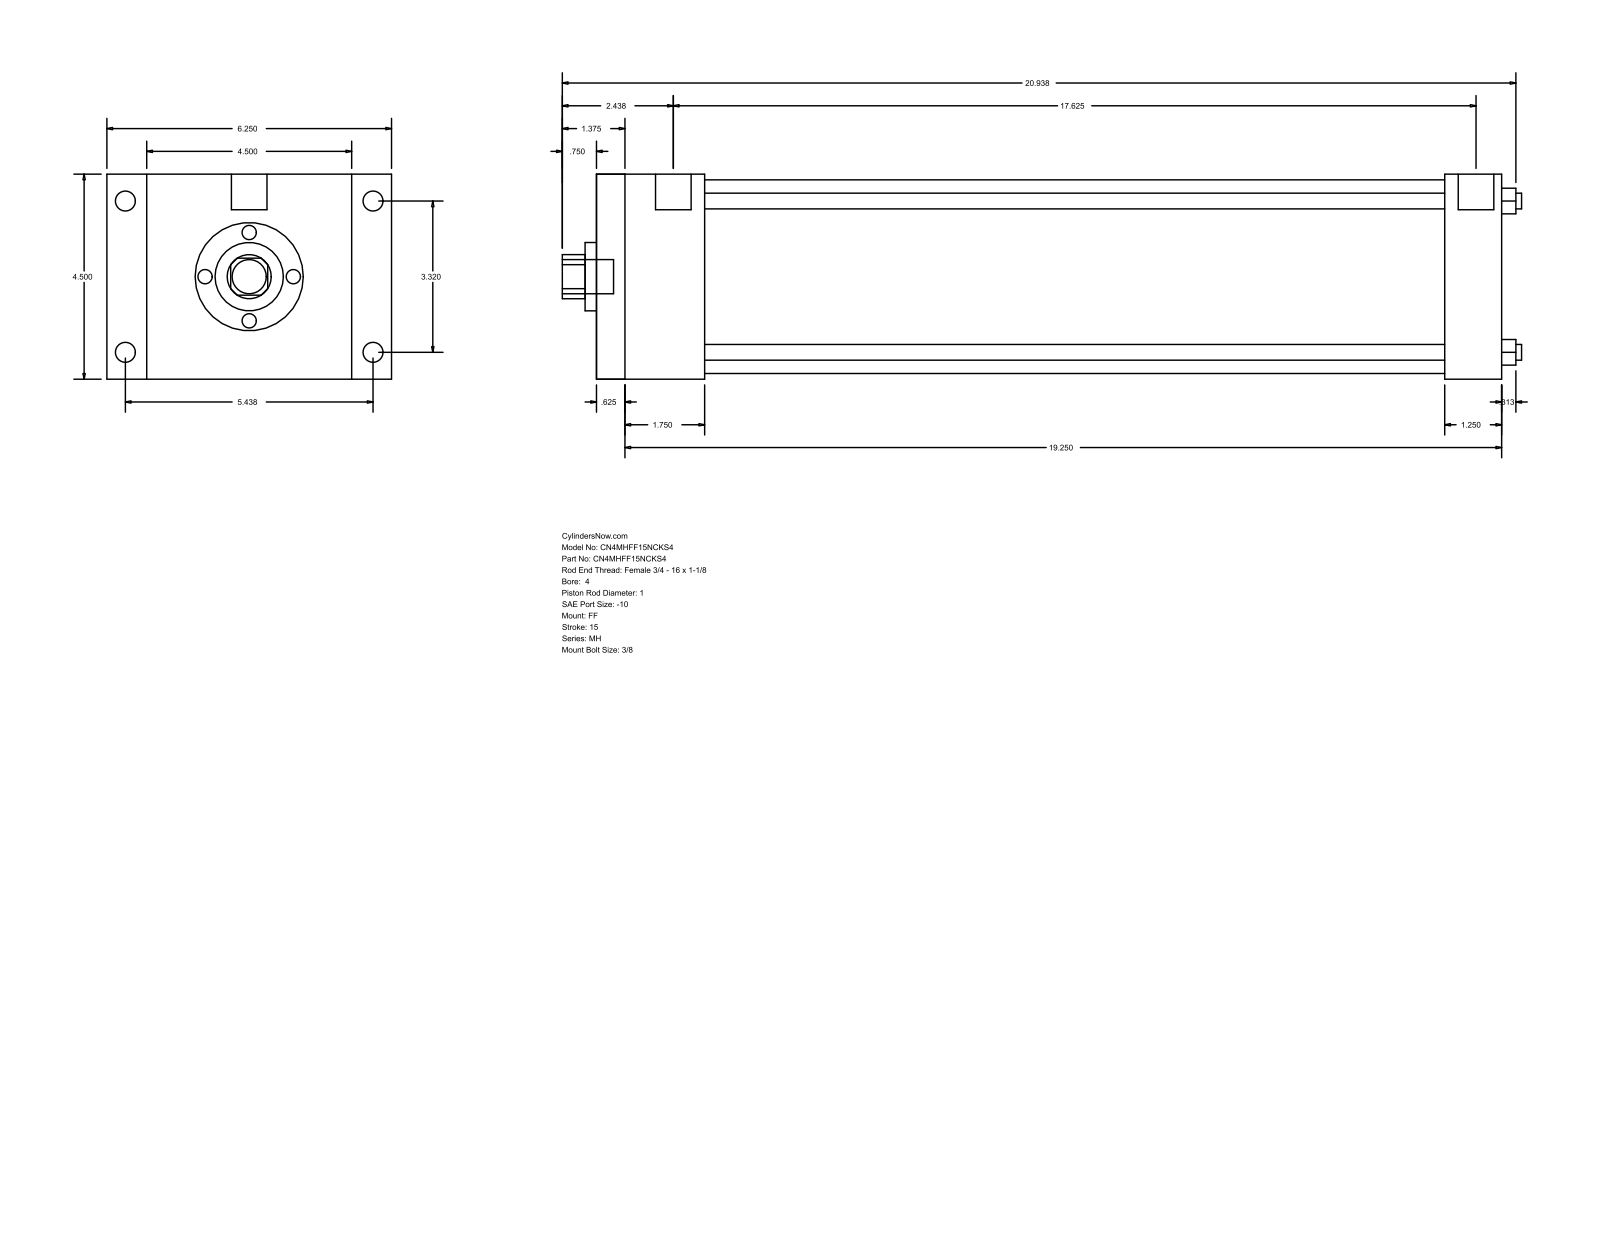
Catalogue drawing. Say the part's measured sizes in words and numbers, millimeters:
The part is named "MH_FF__0400_1". Its 3-D file was written by "GSSL Pune (CONFIG_CONTROL_DESIGN)". It is 0 solids with 92 faces: 64 planar, 28 cylindrical and 0 other. Overall it measures 534.99 by 158.75 by 114.3 millimeters. Round holes: 4 of diameter 8.76, 1 of diameter 25.4, 1 of diameter 38.1, 1 of diameter 107.95. Round bosses or shafts: 4 of diameter 11.13, 4 of diameter 8.73, 2 of diameter 19.84, 1 of diameter 19.05. Partial cylindrical surfaces (rounded edges, fillets, slot ends): 1 of radius 12.29. The main face-to-face distances are 114.3, 504.83, 15.87, 488.96, 60.33, 44.46, 444.5, 473.07, 457.2, 412.74. The hole center spacings are 59.62, 84.32, 119.25.
